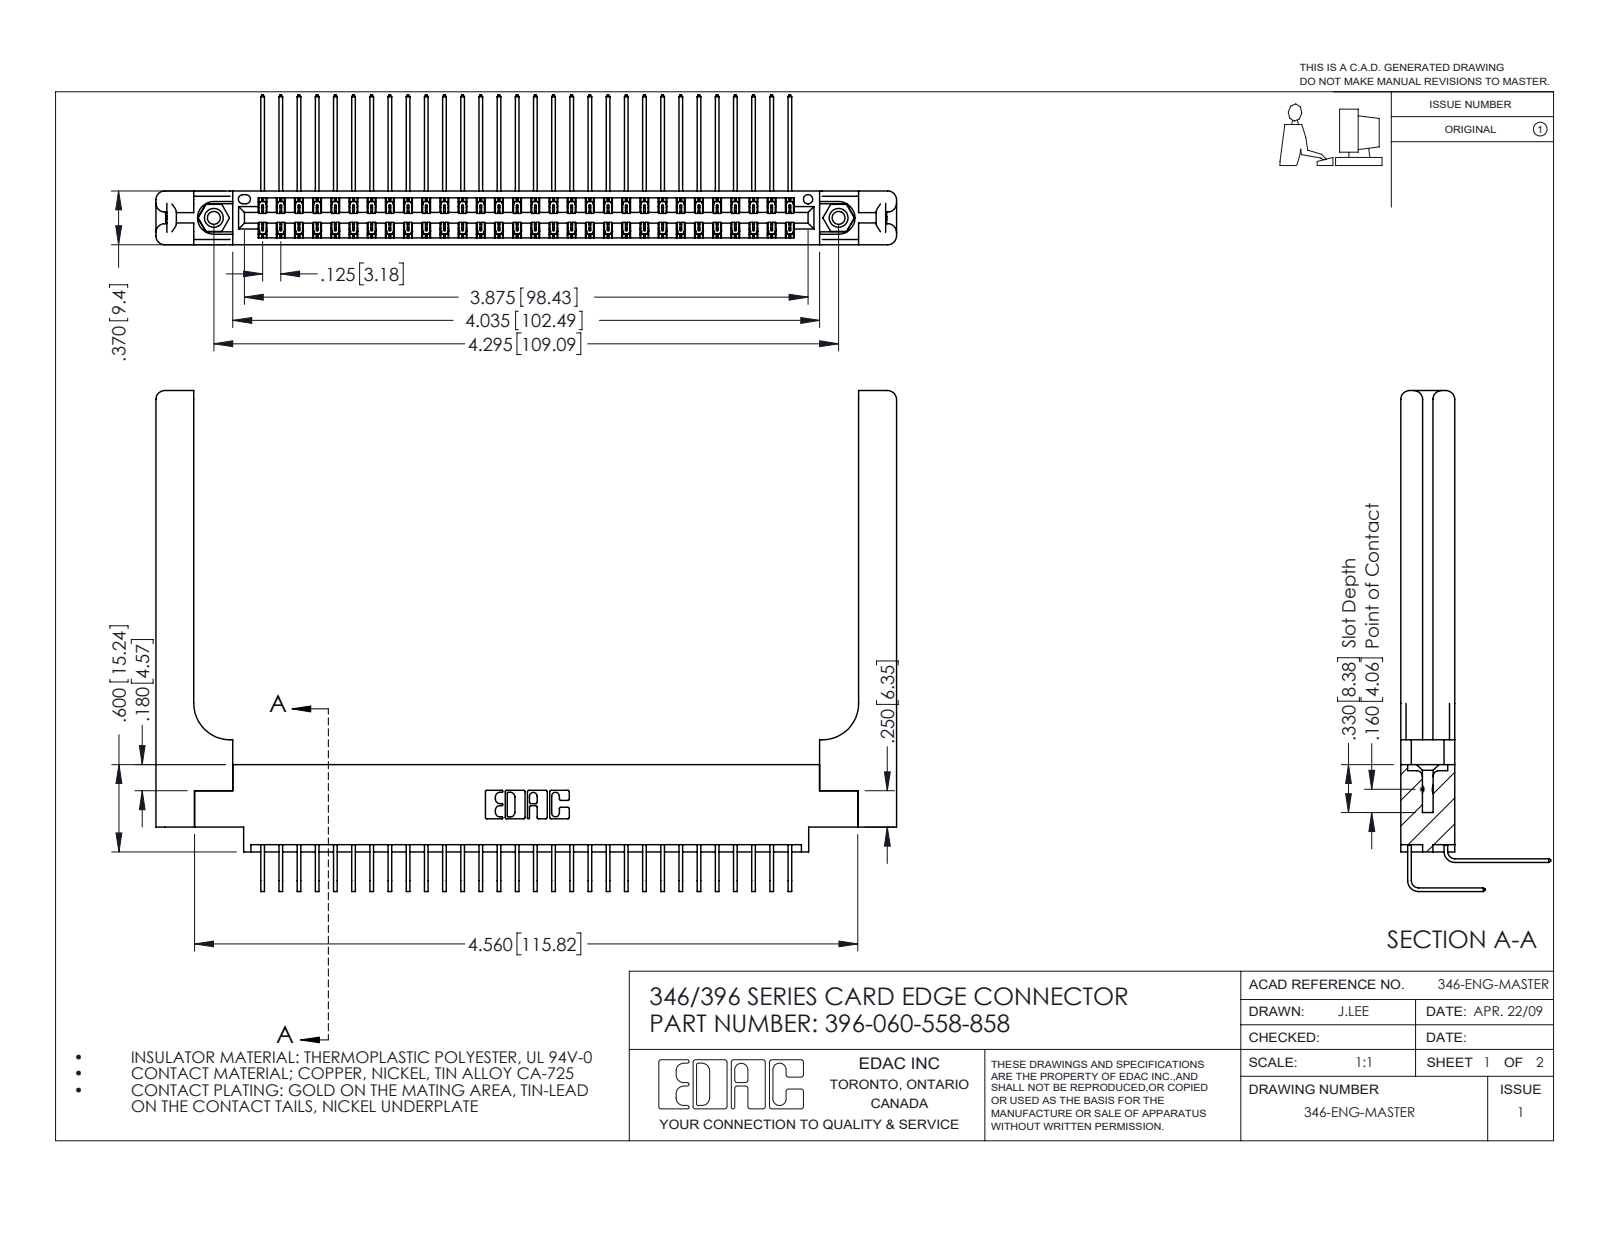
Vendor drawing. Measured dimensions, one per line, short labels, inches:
name: 346 Part_0.170 Offset - 0.156 Dia-TH; 345-292-001_558 559 Tail - 1; 345-250-001_345-250-001-102; 345-292-001_558 Tail - 2 (+2 more)
written by: SolidWorks 2016 (CONFIG_CONTROL_DESIGN)
unit: in
bodies: 65 solids, 3622 faces (2448 planar, 1114 cylindrical, 60 other)
size: 5.091 × 3.443 × 1.03
volume: 1.233 in³; area: 37.34 in²
holes: 2× ⌀0.089, 2× ⌀0.125, 2× ⌀0.156, 1× ⌀0.064
bosses: 2× ⌀0.155
rounds: 90× R0.006, 22× R0.01, 16× R0.06, 6× R0.007, 6× R0.031, 3× R0.026, 2× R0.014, 2× R0.022
face distances: 0.37, 0.322, 0.048, 0.072, 0.025, 0.148, 0.15, 0.298, 0.25, 0.275
hole spacings: 0.246, 4.087, 4.295
